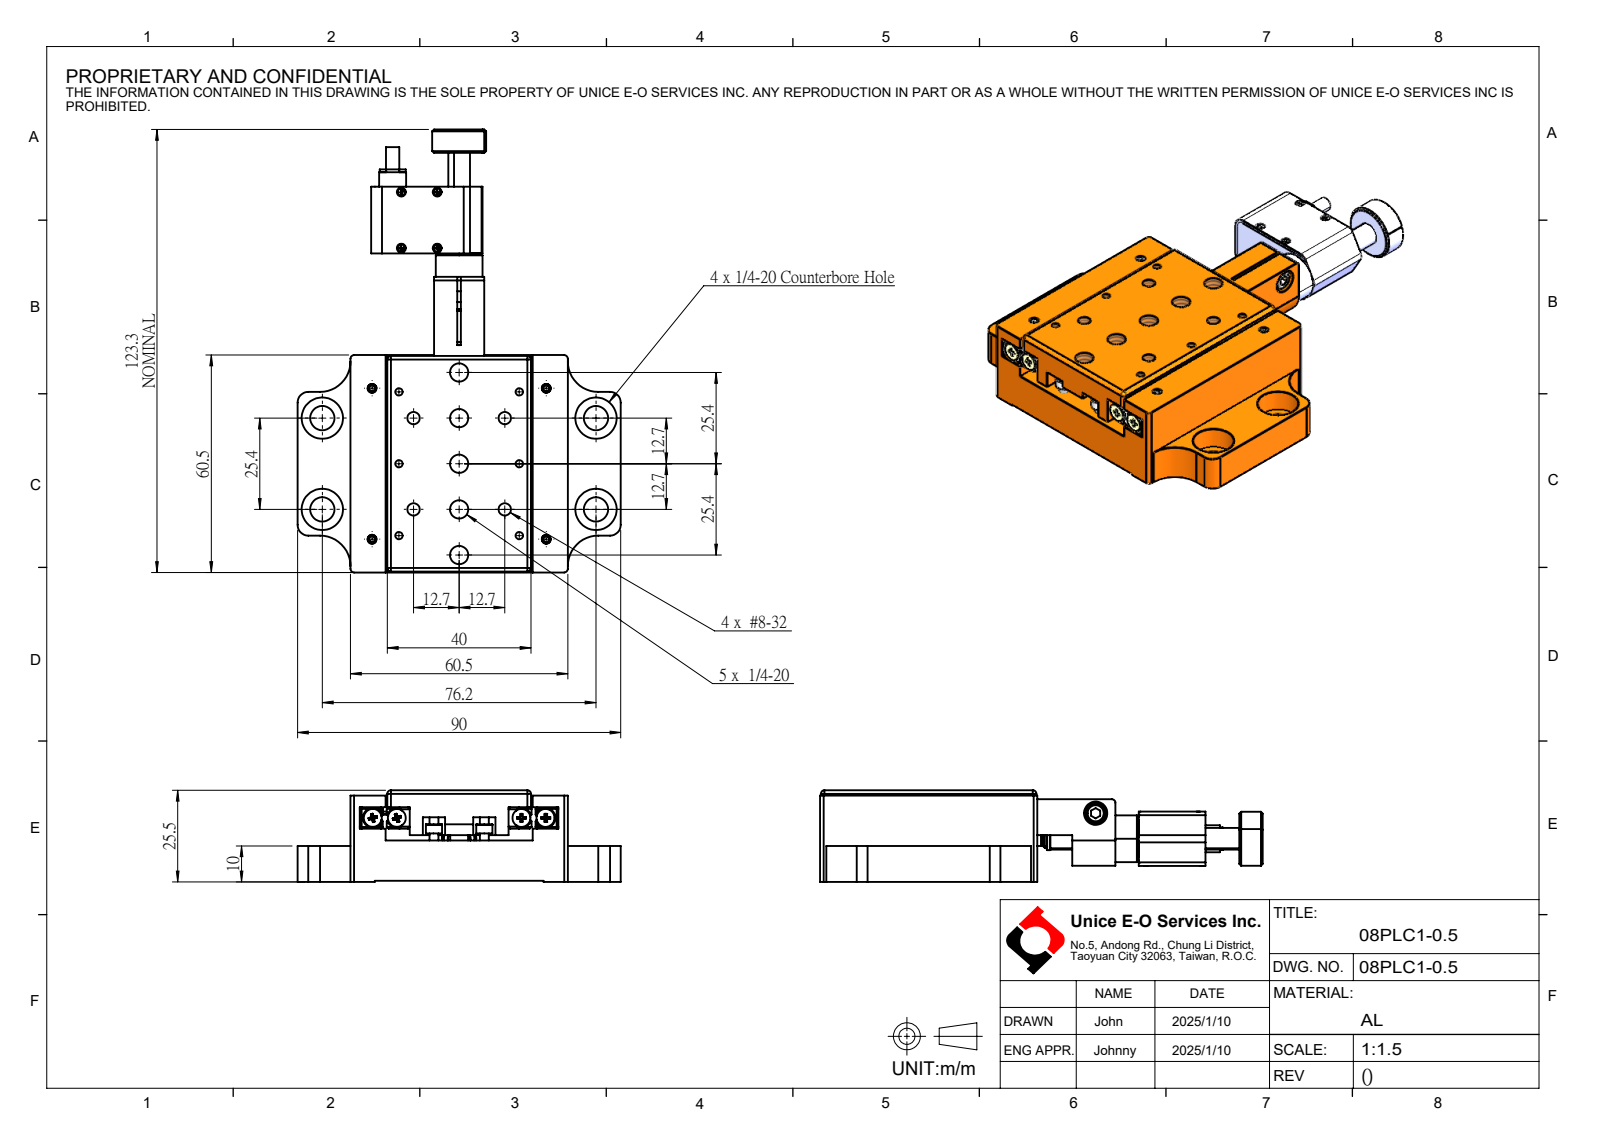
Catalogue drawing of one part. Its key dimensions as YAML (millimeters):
part_name: "08PLC1-0.5"
step_written_by: "SolidWorks 2024 (CONFIG_CONTROL_DESIGN)"
units: millimeters
bodies: {solids: 0, faces: 696, planar: 416, cylindrical: 162, other: 118}
overall_size: [123.27, 90, 25.5]
round_holes:
  - {diameter: 2.5, count: 8}
  - {diameter: 2.05, count: 6}
  - {diameter: 5.11, count: 5}
  - {diameter: 3.45, count: 4}
  - {diameter: 6.76, count: 4}
  - {diameter: 11.51, count: 4}
  - {diameter: 2, count: 2}
  - {diameter: 5.6, count: 1}
  - {diameter: 6.5, count: 1}
  - {diameter: 7.5, count: 1}
  - {diameter: 8, count: 1}
  - {diameter: 9.5, count: 1}
round_bosses_or_shafts:
  - {diameter: 5, count: 5}
  - {diameter: 4.5, count: 2}
  - {diameter: 2.5, count: 2}
  - {diameter: 2, count: 2}
  - {diameter: 15, count: 1}
  - {diameter: 6.4, count: 1}
  - {diameter: 6, count: 1}
  - {diameter: 5.5, count: 1}
partial_cylinders:
  - {radius: 1, count: 13}
  - {radius: 3, count: 6}
  - {radius: 8.5, count: 4}
  - {radius: 2, count: 3}
  - {radius: 7, count: 1}
face_to_face_distances: [14, 1.5, 6, 11.2, 11.5, 25.2, 25.5, 3.2, 12.5, 6.75]
hole_center_spacings: [25.4, 40.16, 12.7, 17.96, 35.92, 38.1, 50.8, 7.57]
